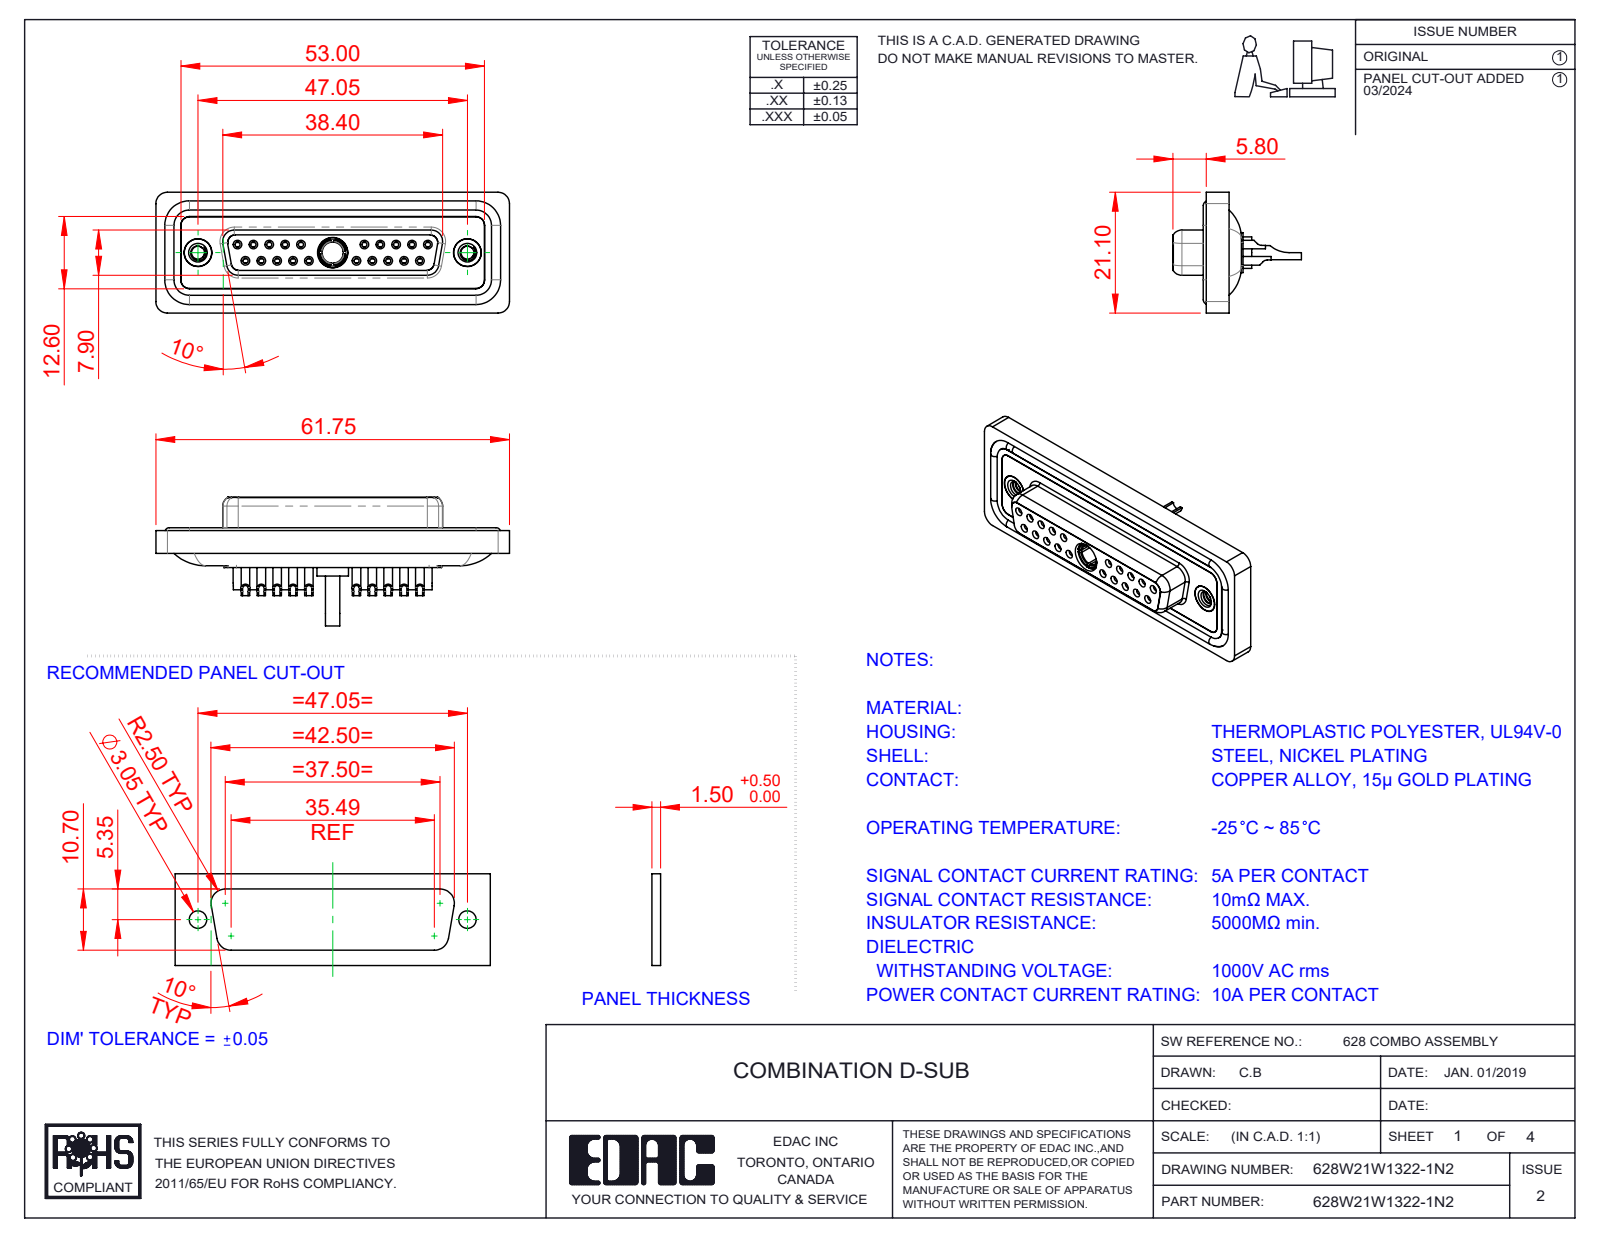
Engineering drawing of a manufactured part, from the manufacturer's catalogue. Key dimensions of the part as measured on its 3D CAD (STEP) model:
Part name (STEP PRODUCT): 628Combo Contact Row 1_22; 628Combo Shell Front_25 Contacts; 628W21W1322-1N2; 628Combo Contact Row 2_22 (+5 more)
STEP written by: SolidWorks 2023 (CONFIG_CONTROL_DESIGN)
Units: millimetres
Bodies: 29 solids, 1565 faces (476 planar, 634 cylindrical, 455 other)
Overall size (bounding box): 61.75 × 22.45 × 21.1
Volume: 8 412 mm³ · Surface area: 14 260 mm²
Round holes (diameter × count): ⌀0.9 ×20, ⌀1 ×20, ⌀1.1 ×20, ⌀1.5 ×20, ⌀2 ×20, ⌀1.6 ×10, ⌀1.7 ×10, ⌀4.85 ×3, ⌀2.26 ×2, ⌀4 ×2, ⌀4.05 ×2, ⌀5 ×2
Round bosses / shafts (diameter × count): ⌀2.2 ×20, ⌀1.6 ×14, ⌀4.95 ×2, ⌀4.8 ×2, ⌀5.5 ×1, ⌀5.2 ×1, ⌀4.96 ×1, ⌀4.75 ×1
Partial cylindrical surfaces — rounded edges, fillets, slot ends (radius × count): R1.5 ×22, R2 ×18, R1.35 ×8, R1.6 ×8, R1 ×6, R0.25 ×4, R0.5 ×4, R0.6 ×4
Main face-to-face distances: 0.4, 1.8, 7.45, 5.65, 6.6, 0.5, 1.6, 7.05, 2.9, 1.1
Hole centre spacings: 3.16, 2.77, 5.54, 5.03, 8.31, 7.48, 16.62, 19.39
